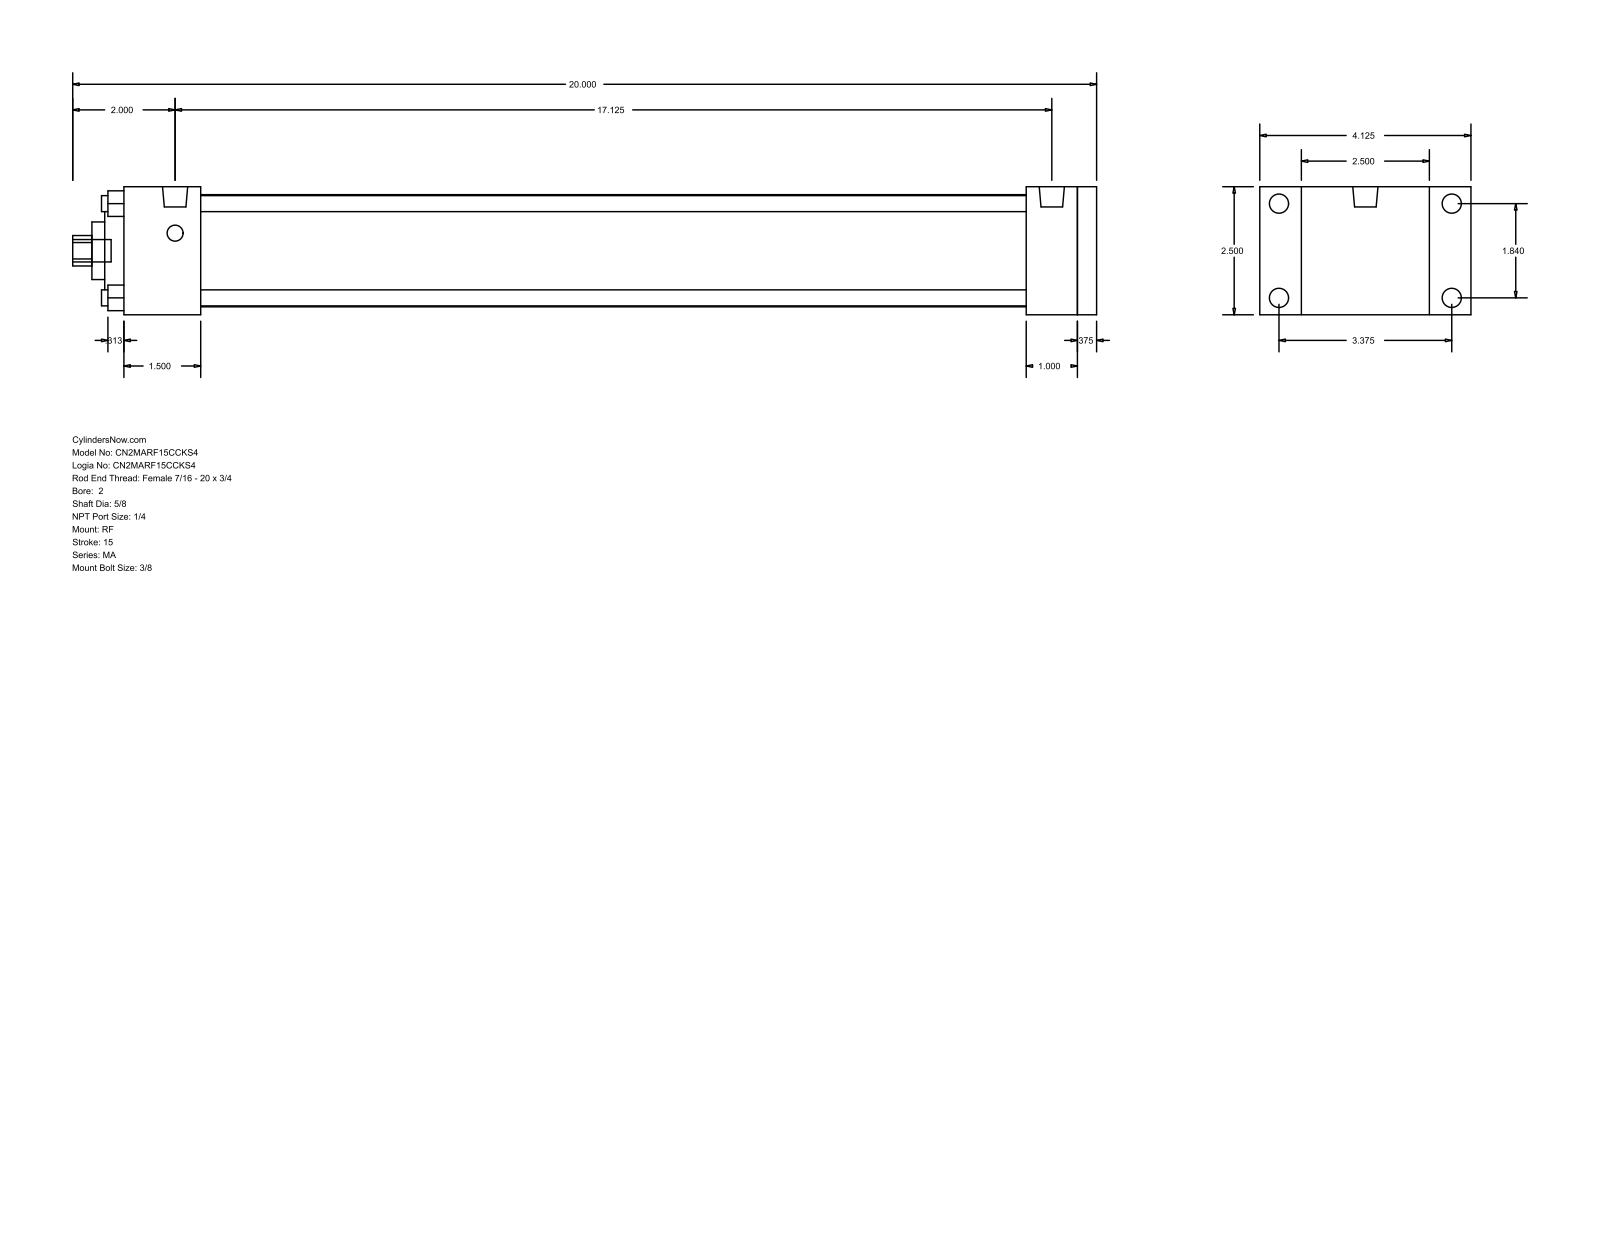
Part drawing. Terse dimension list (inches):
name: MA_RF__0200_0.625
written by: GSSL Pune (CONFIG_CONTROL_DESIGN)
unit: in
bodies: 0 solids, 94 faces (65 planar, 29 cylindrical, 0 other)
size: 20 × 4.125 × 2.5
holes: 4× ⌀0.313, 1× ⌀0.625, 1× ⌀1.125, 1× ⌀2, 1× ⌀2.19
bosses: 4× ⌀0.375, 4× ⌀0.313, 2× ⌀0.492, 1× ⌀0.437
rounds: 1× R0.297
face distances: 2.5, 0.375, 19, 1.5, 18.625, 17.125, 17.5, 17.625, 16.125, 1
hole spacings: 1.301, 1.84, 2.602
